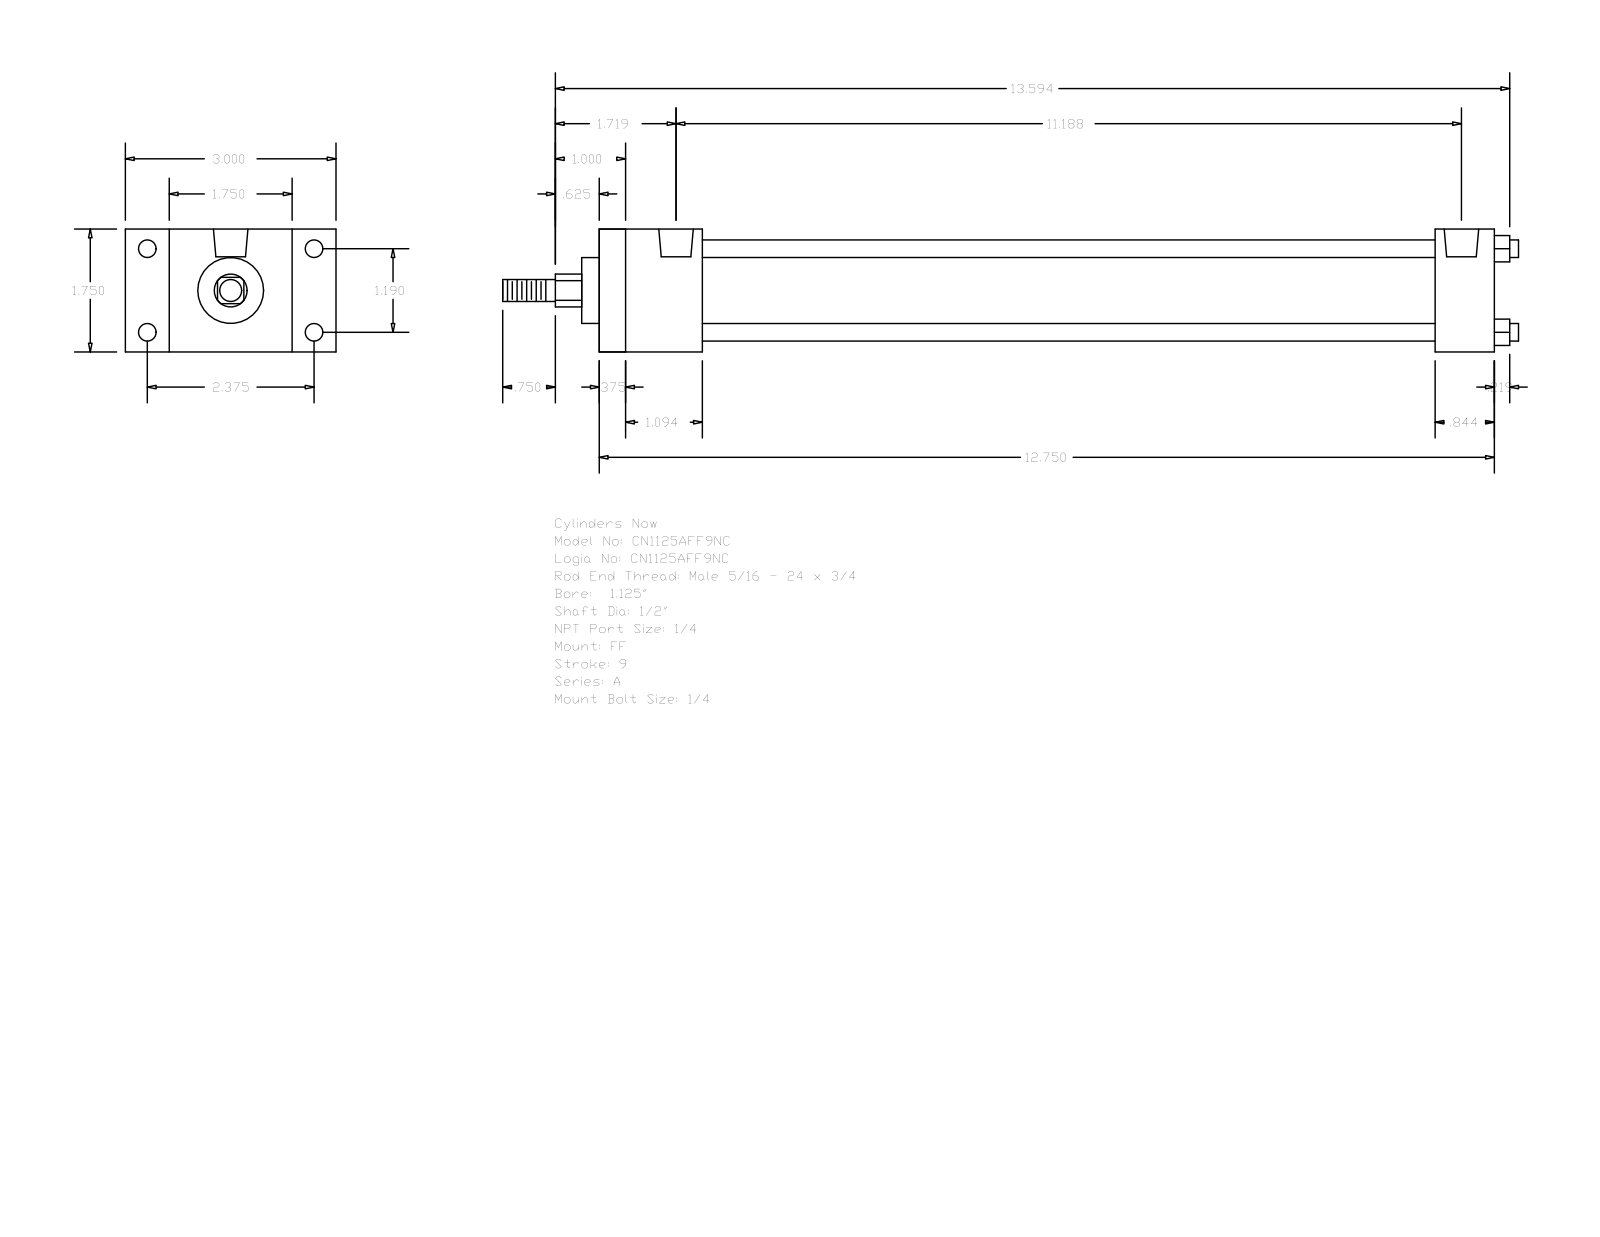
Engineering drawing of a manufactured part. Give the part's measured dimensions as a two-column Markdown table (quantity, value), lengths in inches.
| quantity | value |
| --- | --- |
| part name | A_FF__0112_0.5 |
| STEP written by | GSSL Pune (CONFIG_CONTROL_DESIGN) |
| units | inches |
| bodies | 0 solids, 92 faces (64 planar, 28 cylindrical, 0 other) |
| overall size | 14.469 × 3 × 1.75 |
| round holes (diameter × count) | 0.219 × 4, 0.25 × 4, 0.492 × 2 |
| round bosses / shafts (diameter × count) | 0.25 × 4, 1.255 × 1, 0.937 × 1, 0.5 × 1, 0.313 × 1 |
| partial cylindrical surfaces (radius × count) | 0.234 × 1 |
| main face-to-face distances | 1.75, 12.75, 0.375, 12.375, 0.625, 11.906, 11.531, 0.844, 1.469, 1.094 |
| hole center spacings | 1.19, 2.375, 2.656, 11.063, 0.062, 0.063, 11.125, 11.125 |
